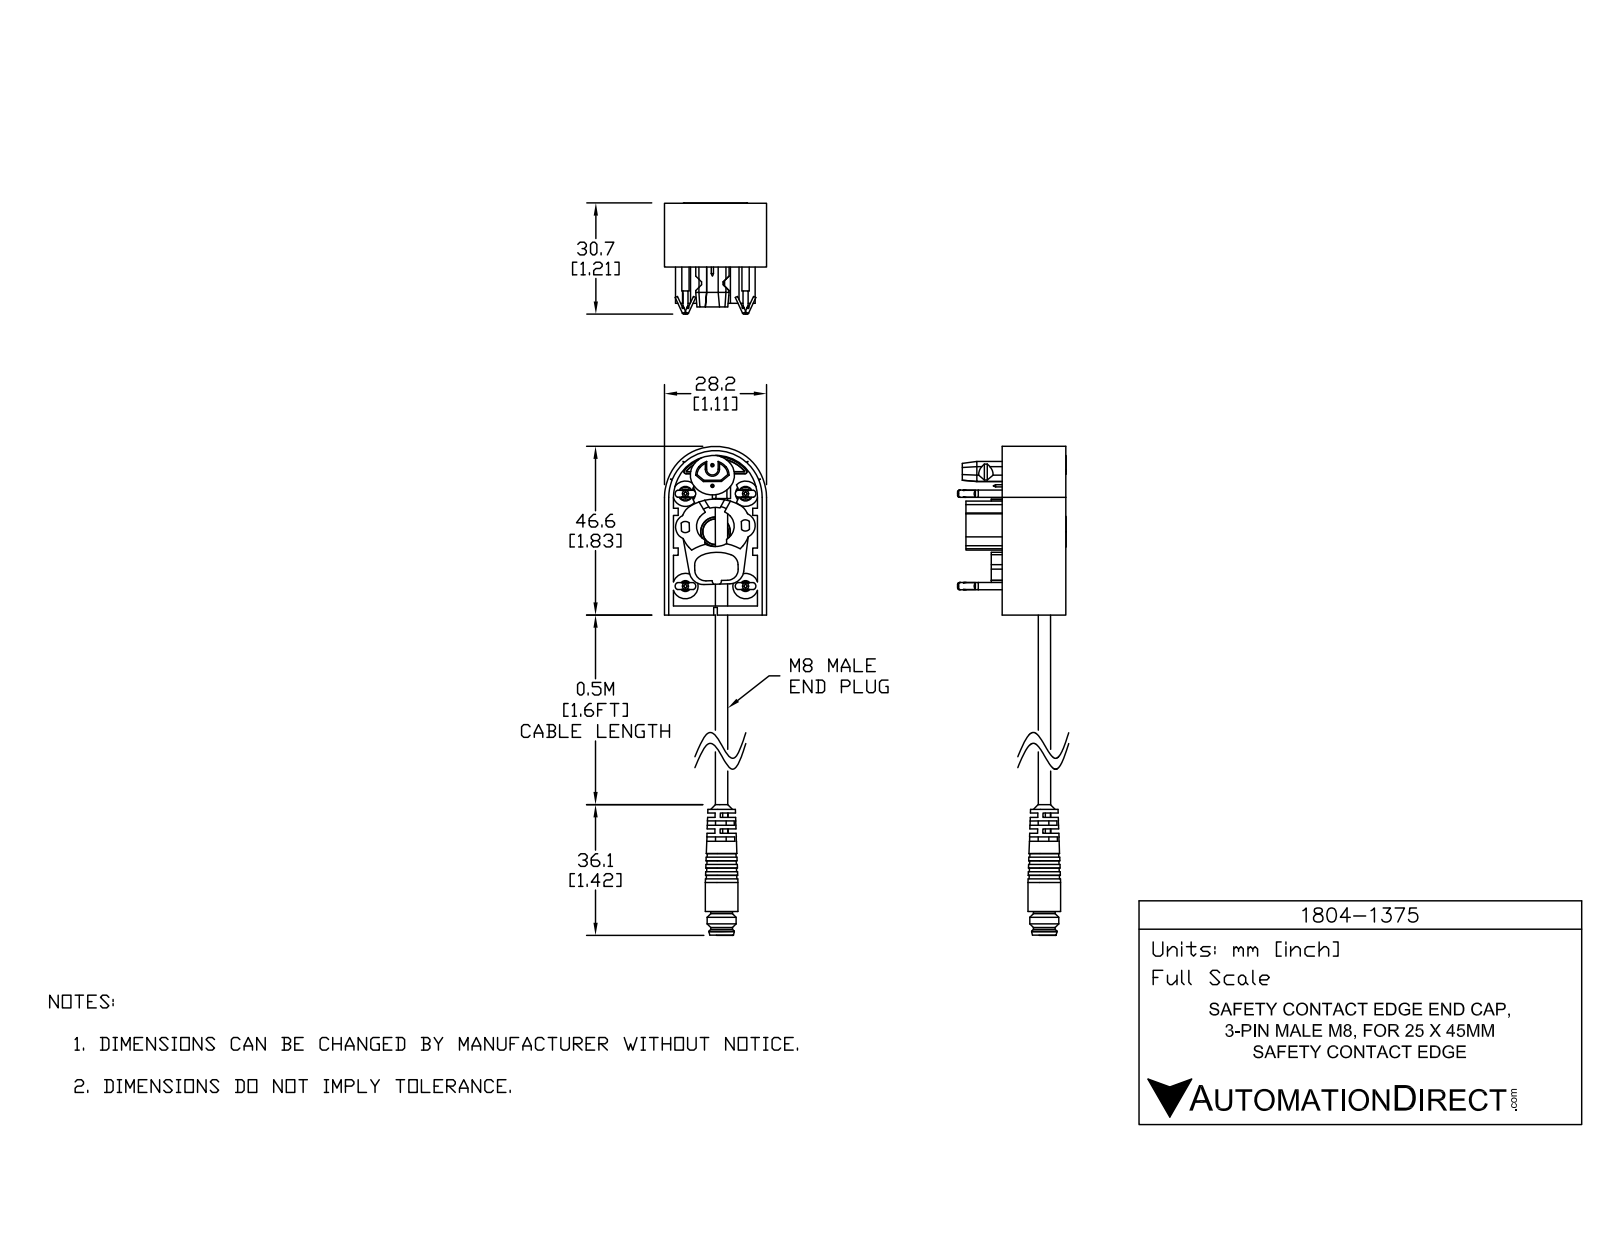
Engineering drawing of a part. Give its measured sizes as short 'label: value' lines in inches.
name: 1804-1375_a
written by: SolidWorks 2018 (AUTOMOTIVE_DESIGN)
unit: in
bodies: 10 solids, 498 faces (256 planar, 159 cylindrical, 83 other)
size: 5.316 × 1.181 × 1.11
volume: 0.891 in³; area: 25.66 in²
holes: 4× ⌀0.02, 4× ⌀0.157, 4× ⌀0.217, 3× ⌀0.138, 2× ⌀0.035, 2× ⌀0.059, 2× ⌀0.118, 2× ⌀0.122, 1× ⌀0.134, 1× ⌀0.228
bosses: 4× ⌀0.197, 4× ⌀0.138, 4× ⌀0.098, 4× ⌀0.079, 3× ⌀0.276, 3× ⌀0.039, 2× ⌀0.236, 2× ⌀0.028
rounds: 16× R0.039, 6× R0.118, 6× R0.138, 6× R0.157, 4× R0.154, 4× R0.197, 2× R0.161, 2× R0.201
face distances: 0.071, 0.039, 0.098, 1.11, 0.031, 0.051, 0.047, 1.012, 1.063, 0.965
hole spacings: 0.654, 0.055, 0.415, 0.816, 0.904, 0.92, 0.924, 0.943
